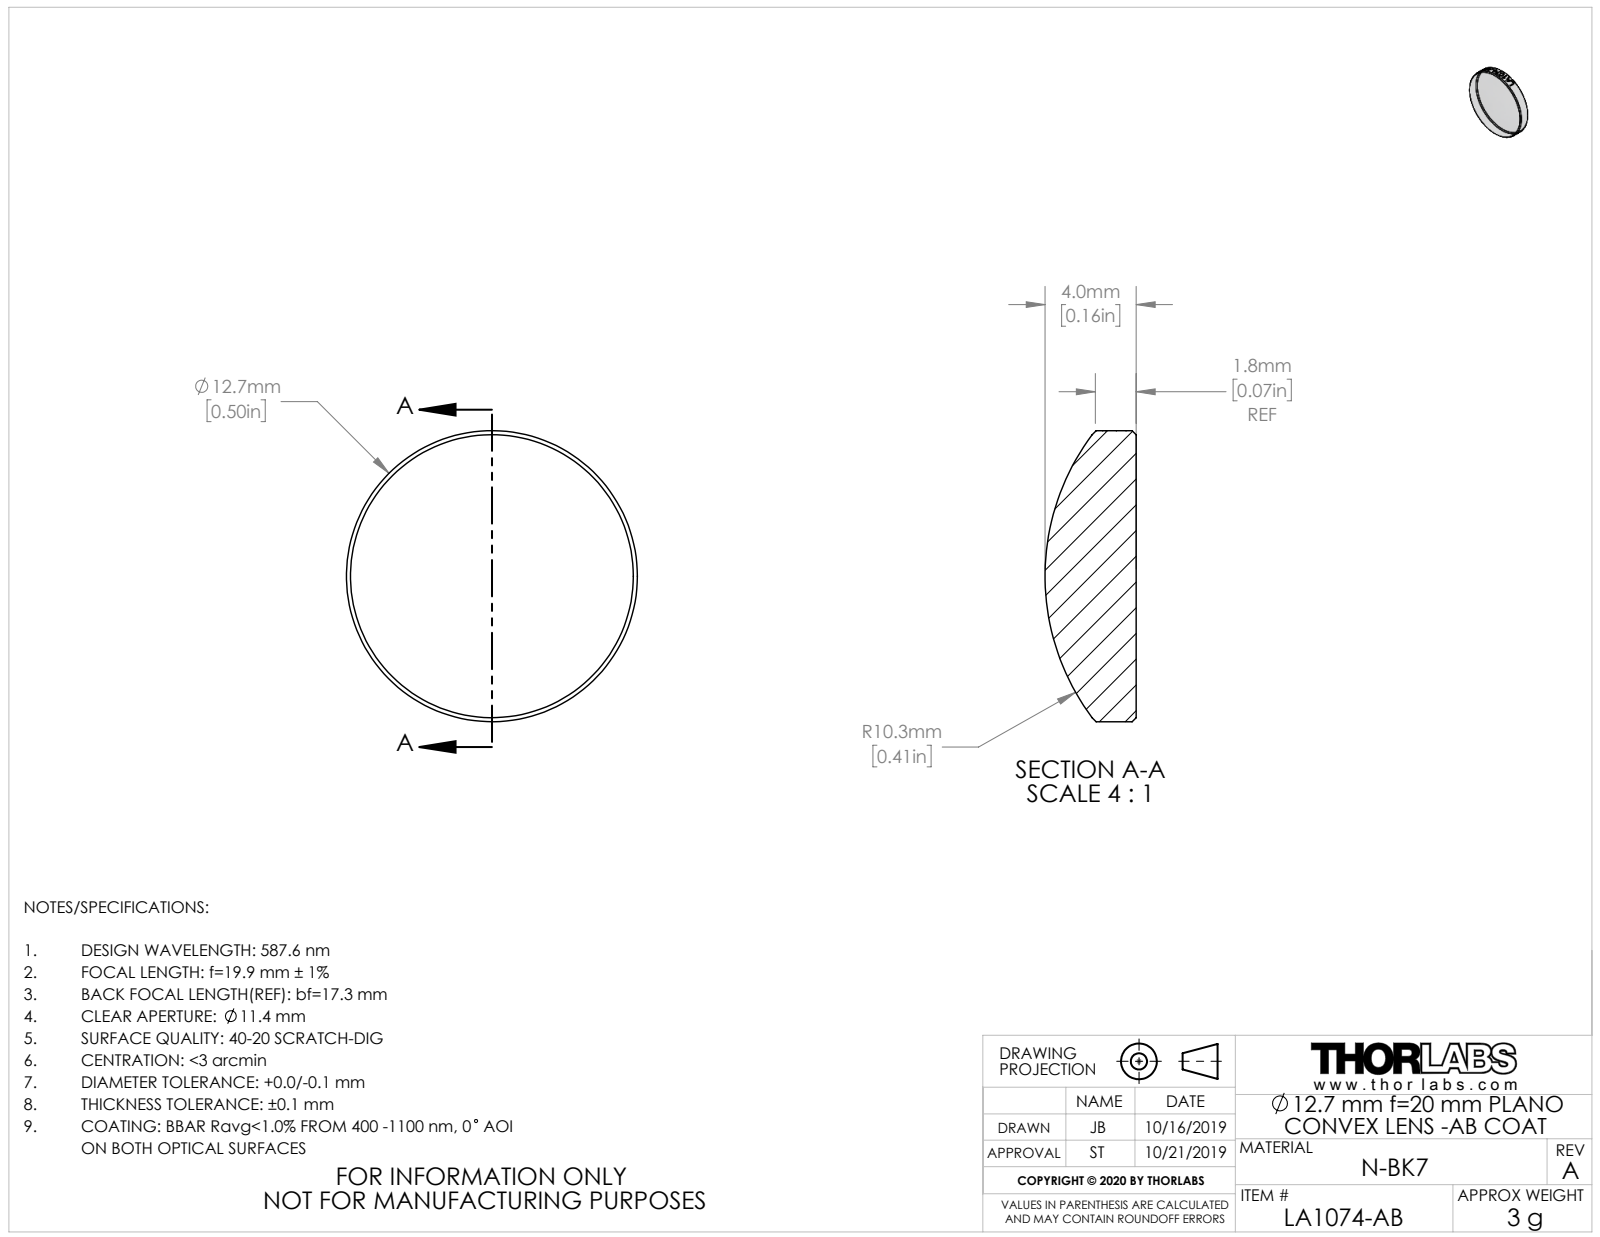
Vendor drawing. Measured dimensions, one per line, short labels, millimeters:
name: TTN195791-E0W
written by: SolidWorks 2018 (CONFIG_CONTROL_DESIGN)
unit: mm
bodies: 1 solid, 28 faces (1 planar, 21 cylindrical, 6 other)
size: 12.7 × 12.7 × 3.98
volume: 370 mm³; area: 335 mm²
bosses: 1× ⌀12.7
